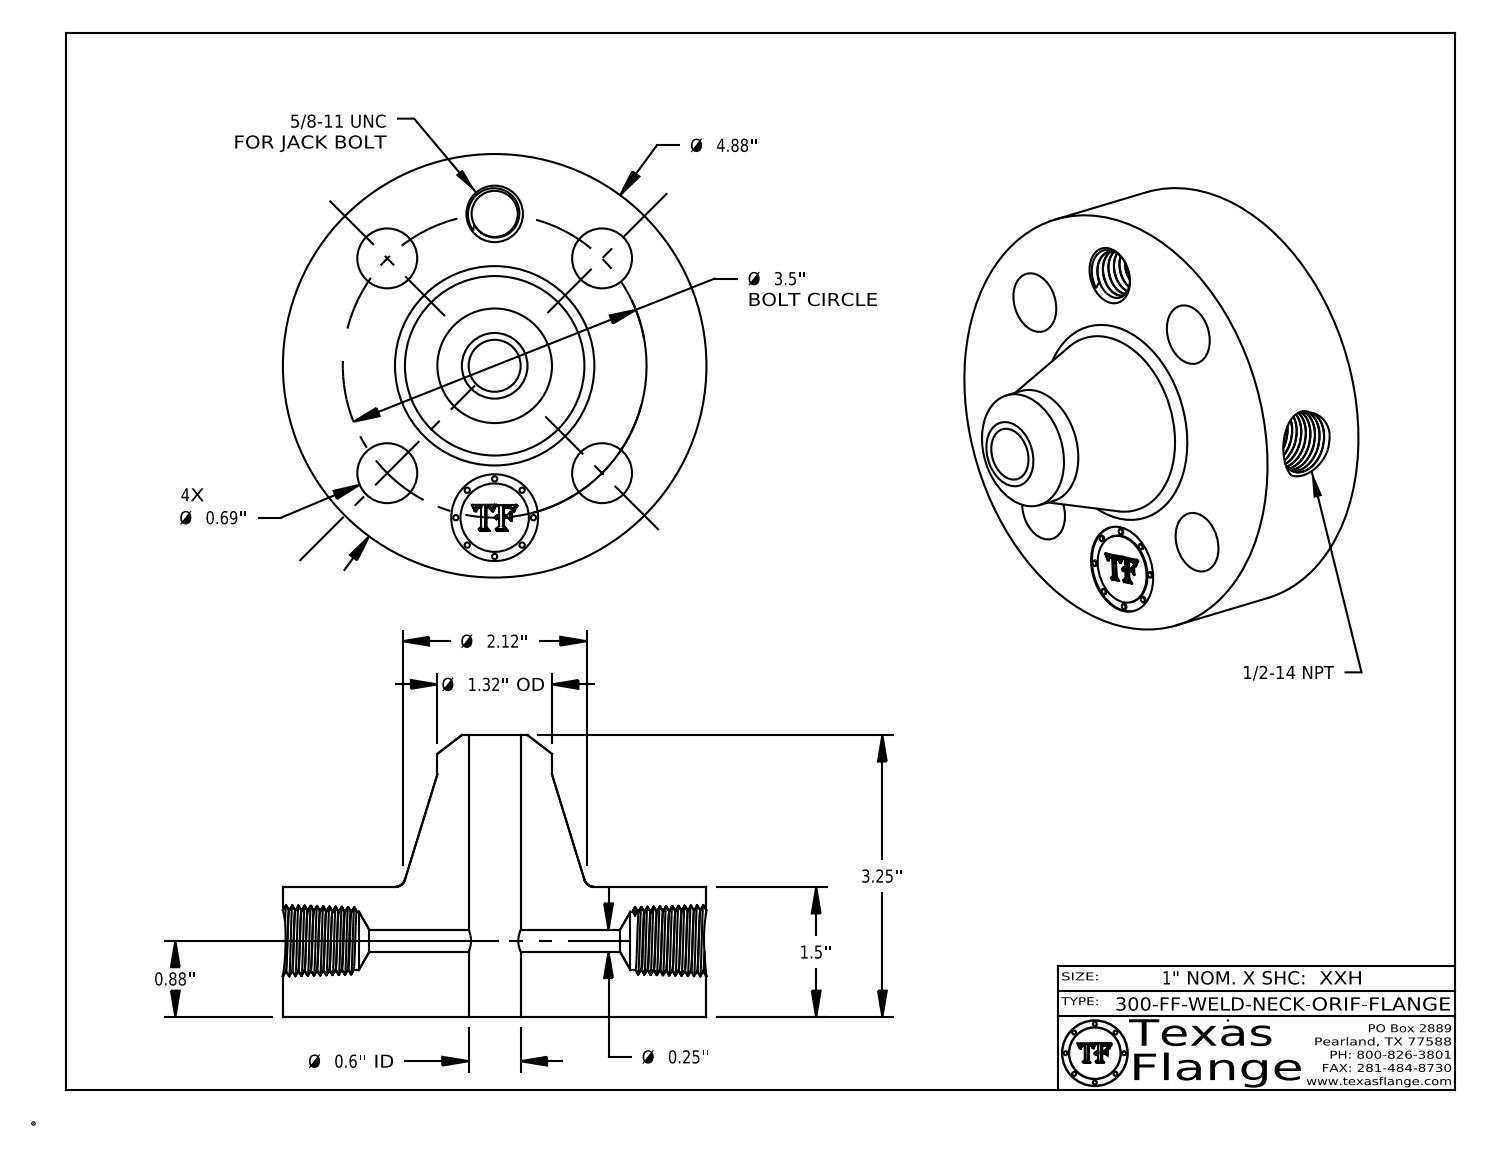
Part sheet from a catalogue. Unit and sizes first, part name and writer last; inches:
Units: inches
Overall size (bounding box): 4.88 × 4.88 × 3.25
Round holes (diameter × count): ⌀0.69 ×4, ⌀0.25 ×1, ⌀0.531 ×1, ⌀0.599 ×1, ⌀0.672 ×1, ⌀1 ×1
Round bosses / shafts (diameter × count): ⌀0.061 ×8, ⌀4.88 ×1, ⌀1.32 ×1, ⌀0.788 ×1
Main face-to-face distances: 1.5, 1.485, 0.015, 3.25, 1.765, 1.75, 0.298, 0.293, 0.054, 0.248
Hole centre spacings: 1.75, 1.339, 2.475, 3.233, 3.5
Volume: 27.19 in³ · Surface area: 94.34 in²
Bodies: 1 solid, 761 faces (368 planar, 85 cylindrical, 308 other)
Part name (STEP PRODUCT): 300-FF-WELD-NECK
STEP written by: CATIA V5 STEP AP214 (AUTOMOTIVE_DESIGN)
